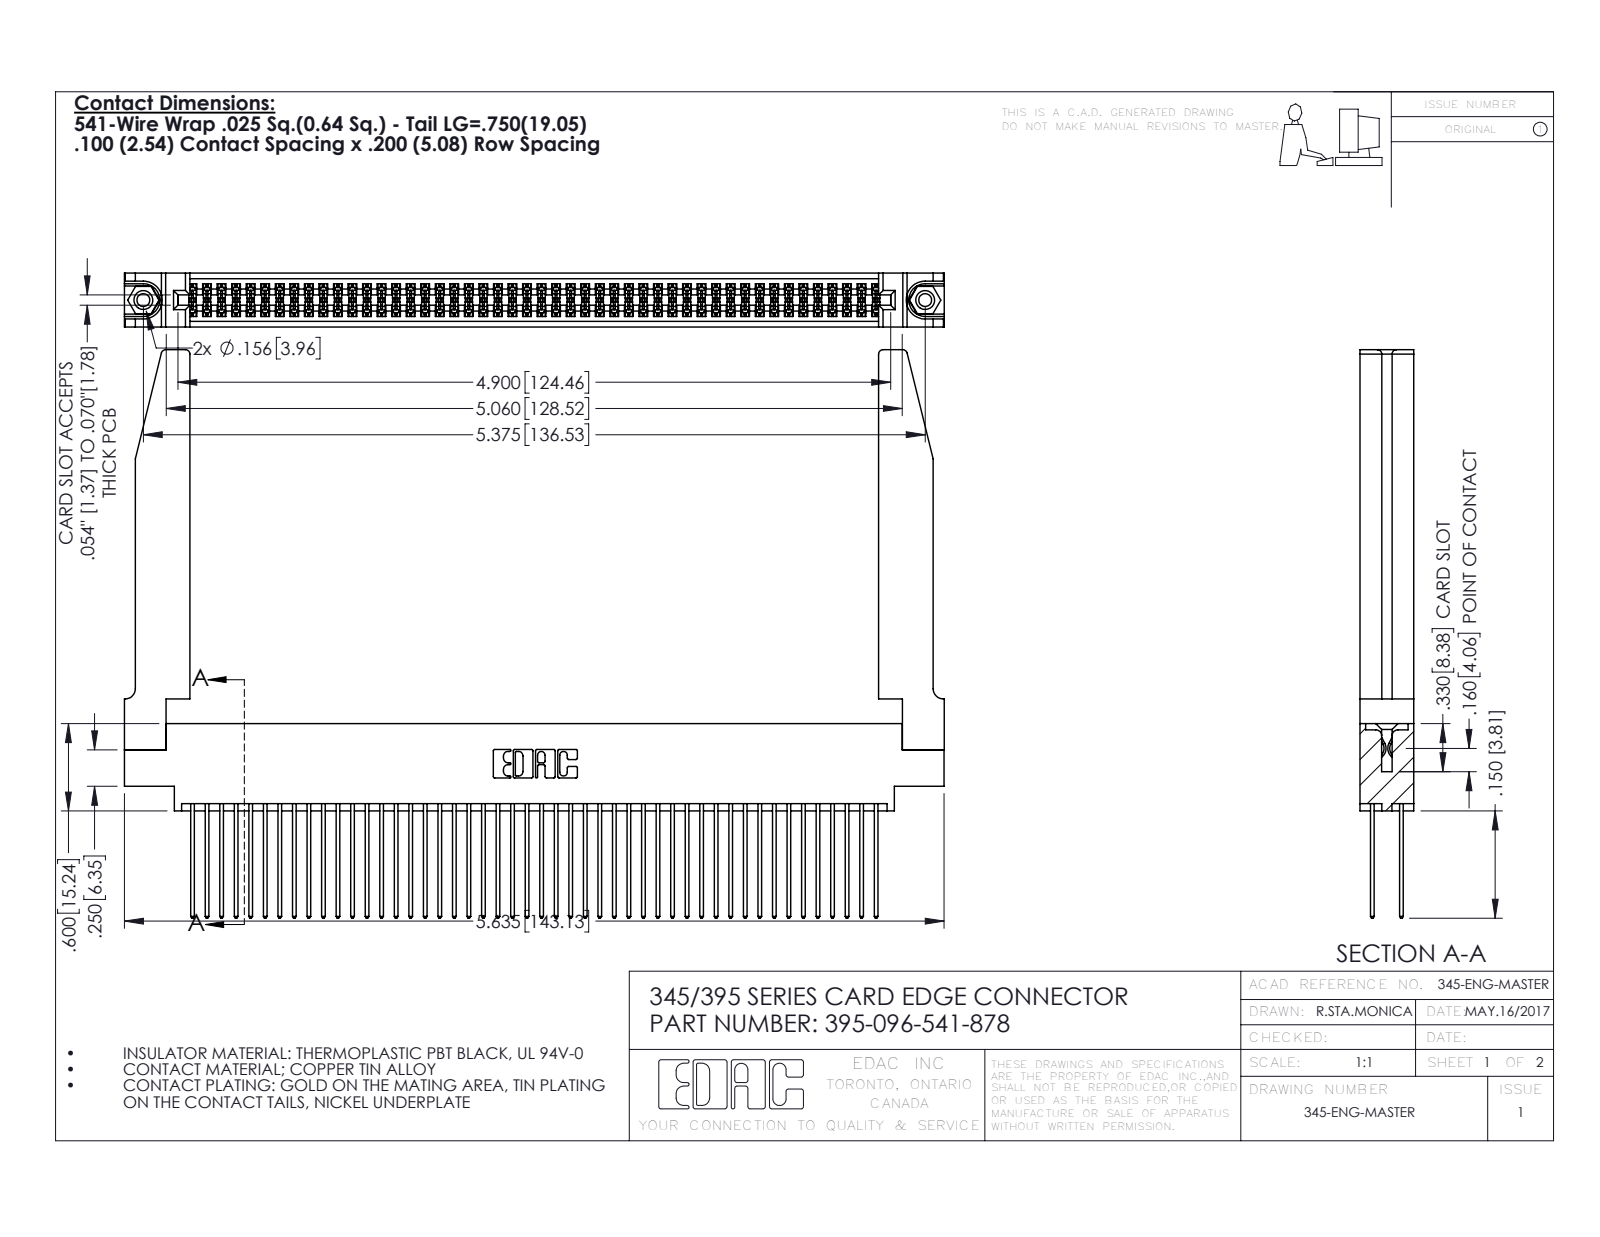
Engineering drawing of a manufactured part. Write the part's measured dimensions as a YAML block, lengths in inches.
part_name: "345-292-001_345-293-141; 345 Part_0.170 Offset - 0.156 Dia-TH; 345-220-078_345-220-078; 395-096-541-878 (+1 more)"
step_written_by: "SolidWorks 2016 (CONFIG_CONTROL_DESIGN)"
units: inches
bodies: {solids: 101, faces: 5164, planar: 3394, cylindrical: 1718, other: 52}
overall_size: [5.636, 3.907, 0.37]
volume: 1.353
surface_area: 48.01
round_holes:
  - {diameter: 0.089, count: 2}
  - {diameter: 0.125, count: 2}
  - {diameter: 0.156, count: 2}
  - {diameter: 0.064, count: 1}
round_bosses_or_shafts:
  - {diameter: 0.155, count: 2}
partial_cylinders:
  - {radius: 0.006, count: 144}
  - {radius: 0.01, count: 96}
  - {radius: 0.01, count: 22}
  - {radius: 0.03, count: 8}
  - {radius: 0.007, count: 6}
  - {radius: 0.031, count: 6}
  - {radius: 0.026, count: 3}
  - {radius: 0.014, count: 2}
face_to_face_distances: [0.072, 0.298, 0.37, 0.098, 0.272, 0.025, 0.2, 0.225, 0.175, 0.15]
hole_center_spacings: [0.27, 5.139, 5.375]
